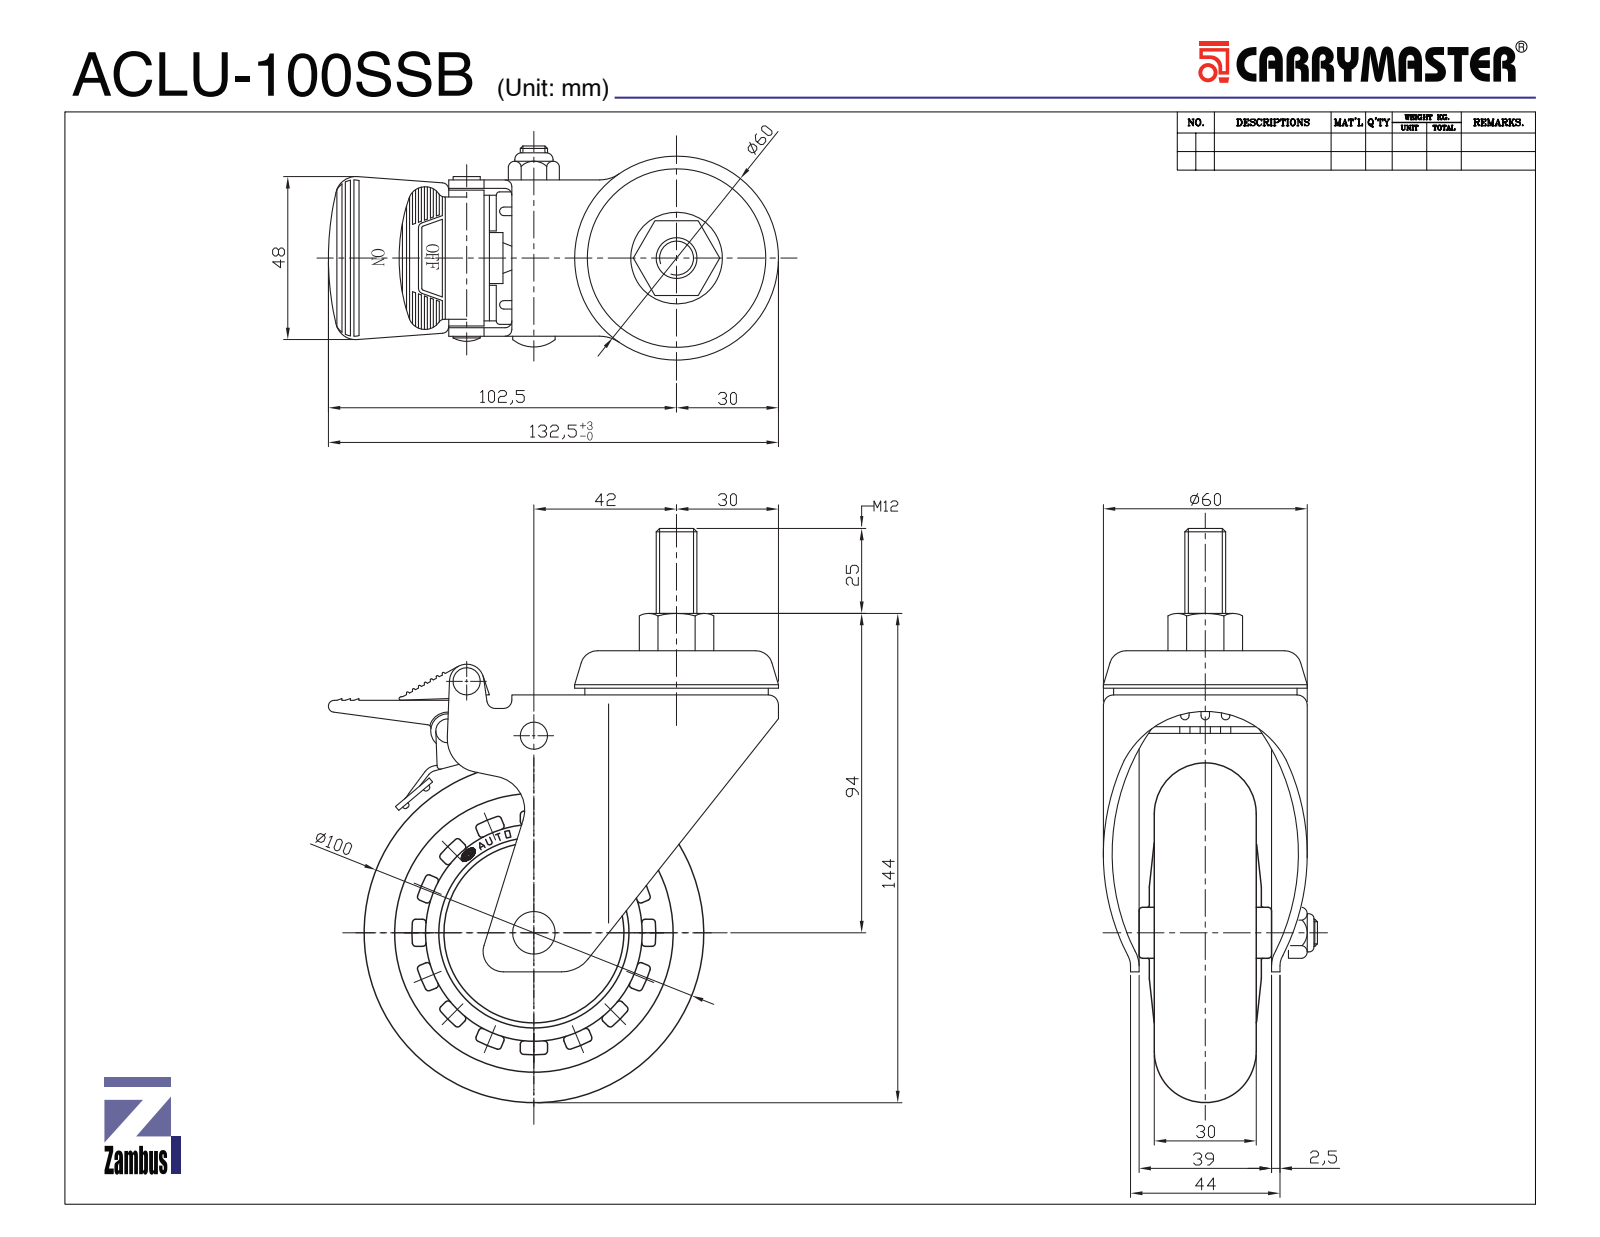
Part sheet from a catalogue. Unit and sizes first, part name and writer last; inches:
Units: inches
Overall size (bounding box): 6.701 × 5.301 × 2.417
Round holes (diameter × count): ⌀0.138 ×2, ⌀0.169 ×2, ⌀0.205 ×2, ⌀0.209 ×1, ⌀0.268 ×1, ⌀0.315 ×1, ⌀0.378 ×1, ⌀0.496 ×1, ⌀0.772 ×1, ⌀0.866 ×1, ⌀1.127 ×1, ⌀1.174 ×1
Round bosses / shafts (diameter × count): ⌀0.354 ×2, ⌀0.193 ×2, ⌀3.228 ×1, ⌀2.583 ×1, ⌀2.35 ×1, ⌀2.165 ×1, ⌀1.575 ×1, ⌀1.244 ×1
Partial cylindrical surfaces — rounded edges, fillets, slot ends (radius × count): R0.039 ×67, R0.008 ×20, R0.152 ×19, R0.394 ×18, R0.079 ×5, R0.276 ×5, R0.118 ×4, R0.059 ×3
Main face-to-face distances: 0.098, 1.713, 0.236, 1.378, 0.335, 1.476, 0.02, 0.217, 0.315, 1.161
Hole centre spacings: 0.382, 0.505, 0.689, 0.691, 1.013, 1.035, 2.284, 2.475
Volume: 16.95 in³ · Surface area: 203.7 in²
Bodies: 20 solids, 1667 faces (893 planar, 467 cylindrical, 307 other)
Part name (STEP PRODUCT): ACLU-100SSB
STEP written by: SolidWorks 2015 (CONFIG_CONTROL_DESIGN)
